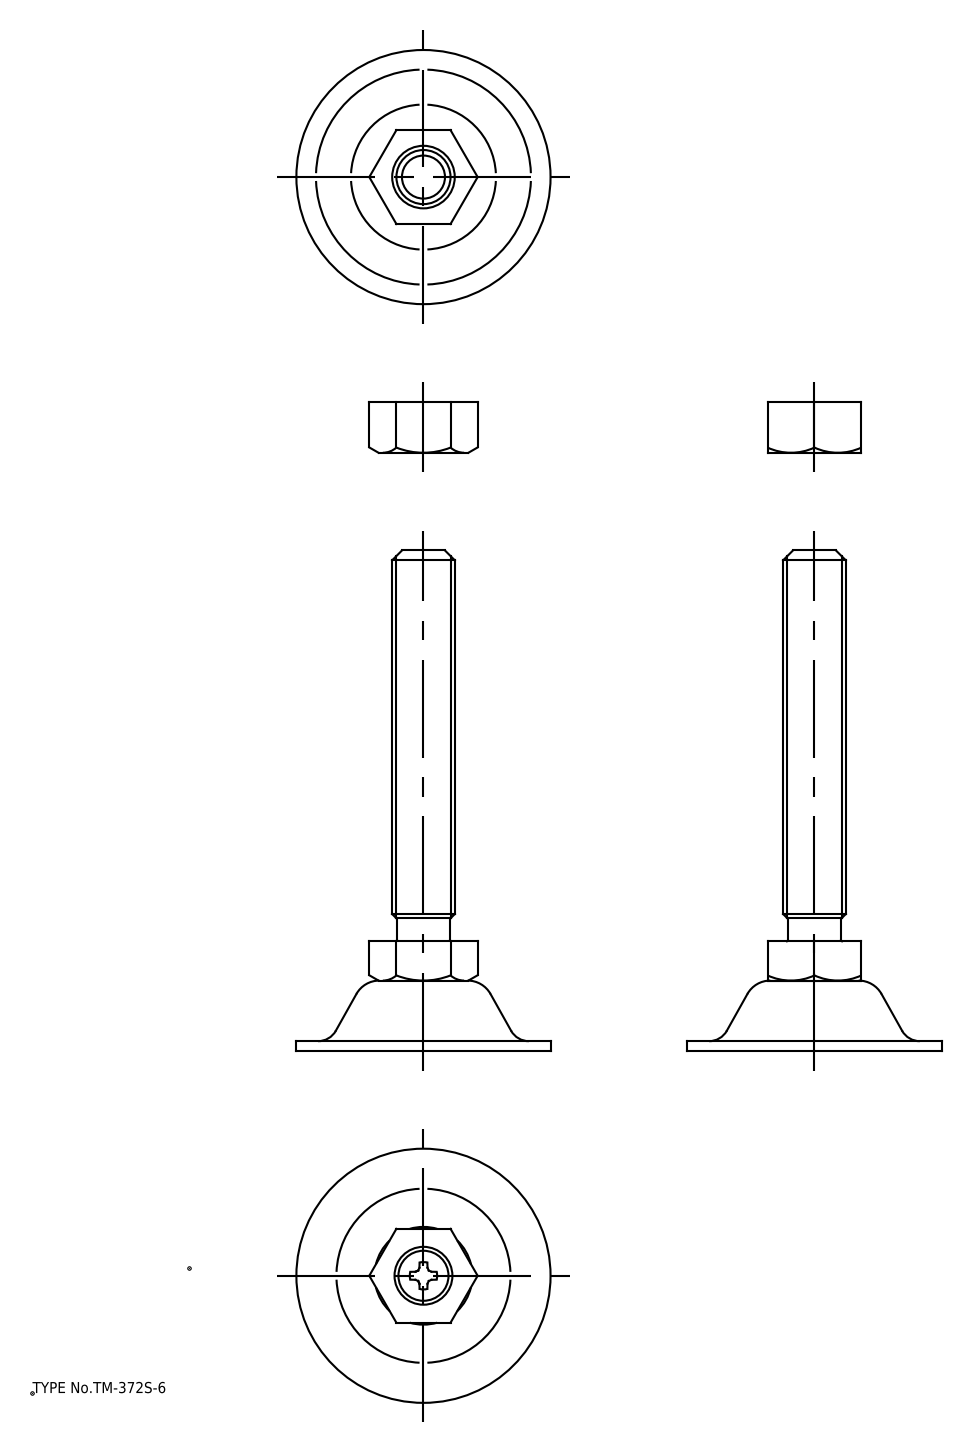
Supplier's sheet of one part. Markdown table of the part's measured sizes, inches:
| quantity | value |
| --- | --- |
| part name | アジャストボルト; フット; ナット |
| STEP written by | spGate 18.9.1 (****-****-****-****) (AUTOMOTIVE_DESIGN) |
| units | inches |
| bodies | 3 solids, 90 faces (48 planar, 18 cylindrical, 24 other) |
| overall size | 5.039 × 2.559 × 2.559 |
| volume | 2.666 in³ |
| surface area | 30.27 in² |
| round holes (diameter × count) | 0.583 × 1, 0.63 × 1 |
| round bosses / shafts (diameter × count) | 2.559 × 1, 0.531 × 1 |
| partial cylindrical surfaces (radius × count) | 0.138 × 1 |
| main face-to-face distances | 0.945, 0.098, 0.512, 0.61, 2.815, 0.157, 0.709, 0.059, 0.551, 2.717 |
